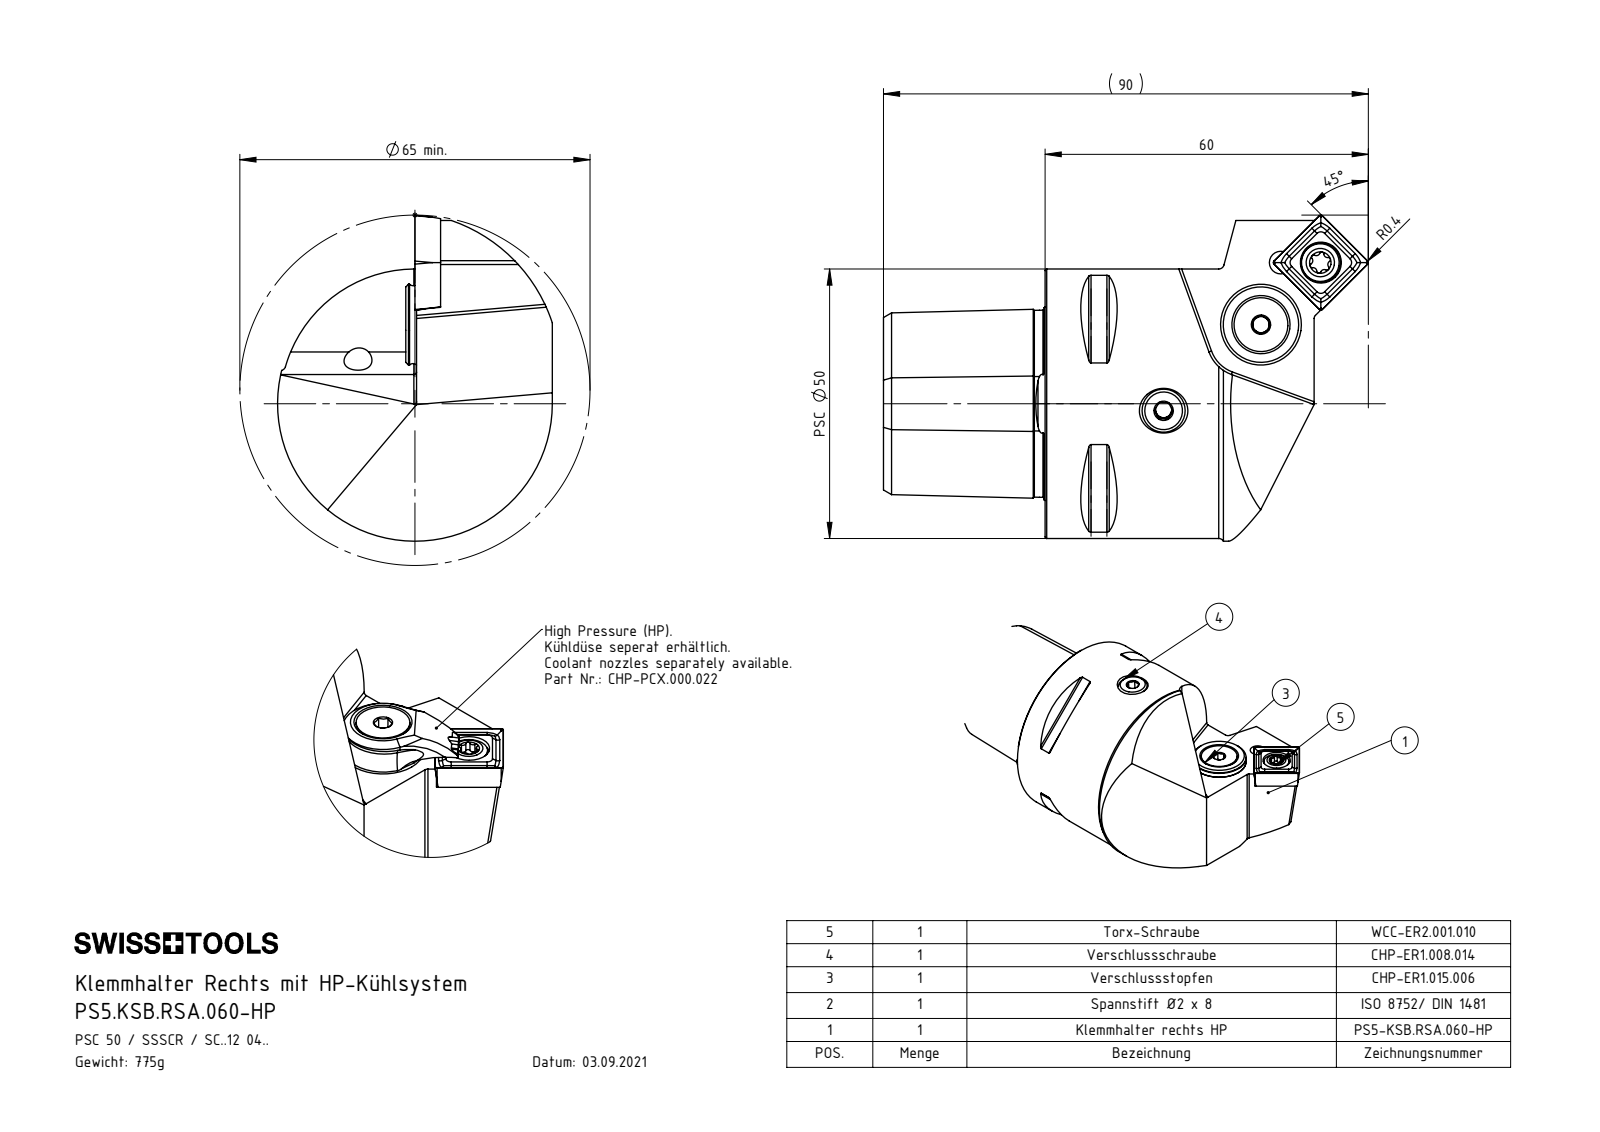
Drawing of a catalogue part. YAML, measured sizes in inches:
part_name: "PS5.KSB.RSA.060-HP; CHP-PCX.000.022_Düse; DIN 7991 - M5x18; SCMT120404 (+7 more)"
step_written_by: "SolidWorks 2022 (CONFIG_CONTROL_DESIGN)"
units: inches
bodies: {solids: 9, faces: 478, planar: 102, cylindrical: 135, other: 241}
overall_size: [3.543, 2.382, 2.008]
volume: 6.049
surface_area: 35.6
round_holes:
  - {diameter: 0.165, count: 4}
  - {diameter: 0.197, count: 2}
  - {diameter: 0.047, count: 1}
  - {diameter: 0.079, count: 1}
  - {diameter: 0.118, count: 1}
  - {diameter: 0.157, count: 1}
  - {diameter: 0.209, count: 1}
  - {diameter: 0.217, count: 1}
  - {diameter: 0.24, count: 1}
  - {diameter: 0.276, count: 1}
  - {diameter: 0.299, count: 1}
  - {diameter: 0.331, count: 1}
round_bosses_or_shafts:
  - {diameter: 0.197, count: 2}
  - {diameter: 1.969, count: 1}
  - {diameter: 0.585, count: 1}
  - {diameter: 0.528, count: 1}
  - {diameter: 0.394, count: 1}
  - {diameter: 0.315, count: 1}
  - {diameter: 0.276, count: 1}
  - {diameter: 0.217, count: 1}
partial_cylinders:
  - {radius: 0.02, count: 12}
  - {radius: 0.039, count: 7}
  - {radius: 0.015, count: 6}
  - {radius: 0.027, count: 6}
  - {radius: 0.236, count: 3}
  - {radius: 0.043, count: 2}
  - {radius: 0.047, count: 2}
  - {radius: 0.197, count: 2}
face_to_face_distances: [1.181, 0.176, 0.817, 0.992, 0.755, 0.815, 0.177, 1.748, 0.059, 0.118]
hole_center_spacings: [0.177, 0.29, 0.294, 0.302, 0.476, 0.493, 0.496, 0.627]
